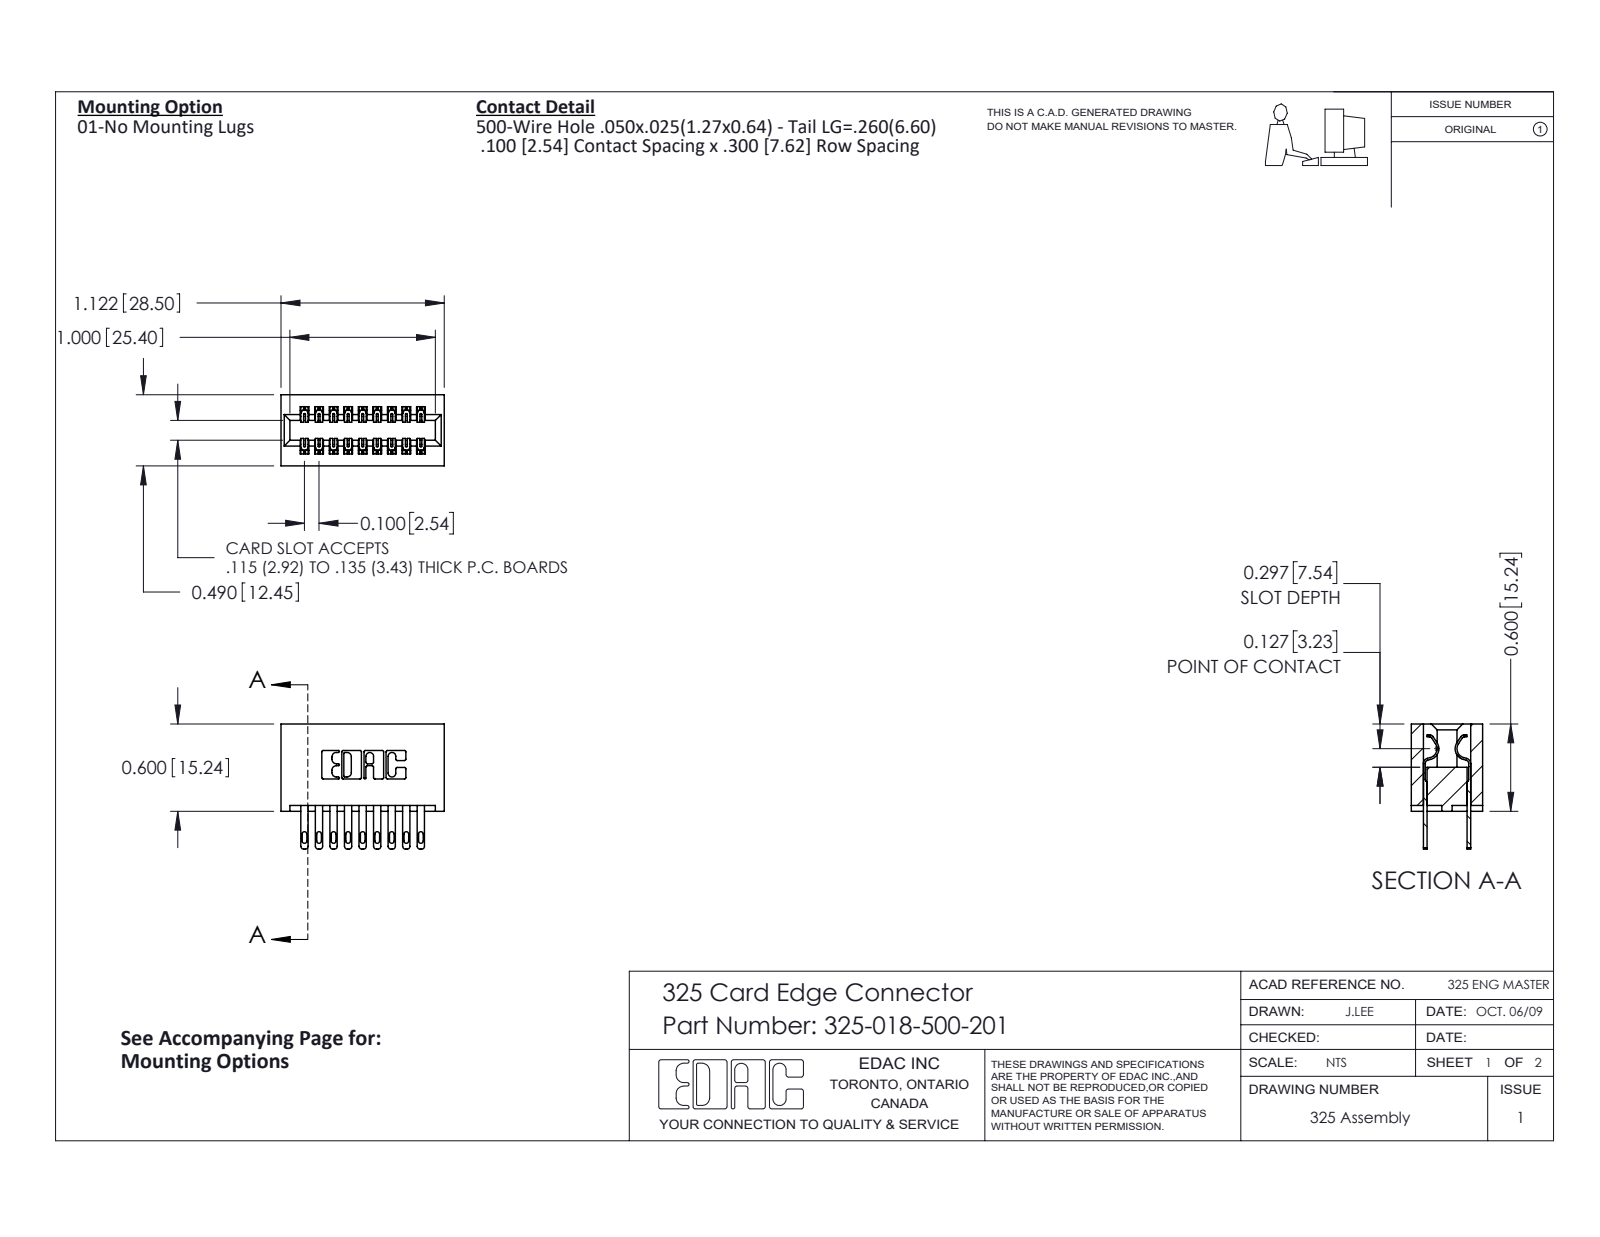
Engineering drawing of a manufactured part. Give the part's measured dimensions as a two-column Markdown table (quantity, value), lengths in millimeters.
| quantity | value |
| --- | --- |
| part name | 325-018-500-201; 325 Part_Lugless; 325-292-001_325-293-100 |
| STEP written by | SolidWorks 2016 (CONFIG_CONTROL_DESIGN) |
| units | millimeters |
| bodies | 19 solids, 970 faces (606 planar, 364 cylindrical, 0 other) |
| overall size | 28.5 × 21.8 × 12.4 |
| volume | 4 050 mm³ |
| surface area | 4 961 mm² |
| partial cylindrical surfaces (radius × count) | 0.2 × 27, 0.3 × 22, 0.4 × 18, 0.5 × 18, 0.2 × 6, 0.8 × 6, 0.7 × 3, 0.4 × 2 |
| main face-to-face distances | 7.6, 2.1, 10.3, 2.5, 5.1, 10.2, 1, 2.7, 9.7, 0.6 |
